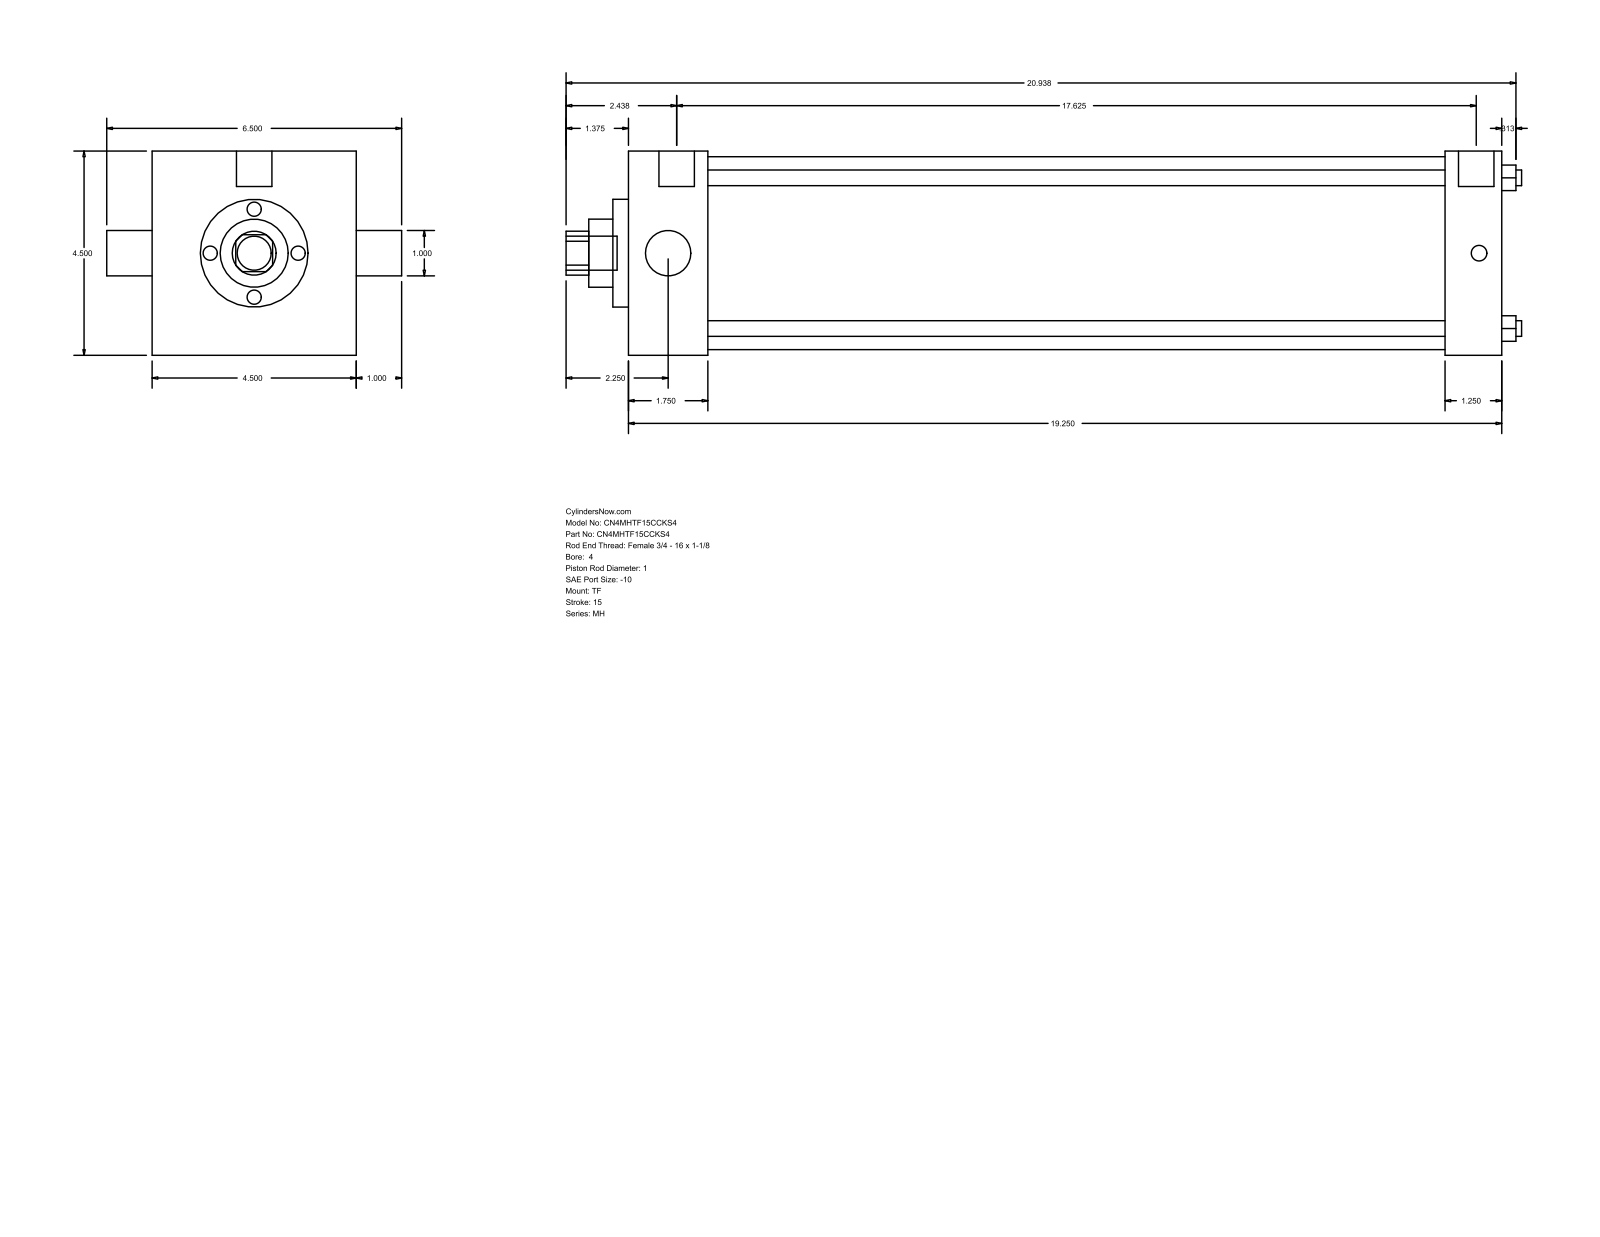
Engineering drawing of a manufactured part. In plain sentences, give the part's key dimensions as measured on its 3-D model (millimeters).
The part is named "MH_TF__0400_1". Its 3-D file was written by "GSSL Pune (CONFIG_CONTROL_DESIGN)". It is 0 solids with 86 faces: 61 planar, 25 cylindrical and 0 other. Overall it measures 534.99 by 165.1 by 114.3 millimeters. Round holes: 4 of diameter 8.76, 2 of diameter 25.4, 1 of diameter 38.1, 1 of diameter 60.33, 1 of diameter 107.95. Round bosses or shafts: 3 of diameter 8.73, 2 of diameter 19.84, 1 of diameter 19.05. Partial cylindrical surfaces (rounded edges, fillets, slot ends): 1 of radius 12.29. The main face-to-face distances are 114.3, 488.96, 44.46, 444.5, 457.2, 412.74, 31.76, 8.73, 53.19, 465.93. The hole center spacings are 59.62, 84.32, 119.25.
